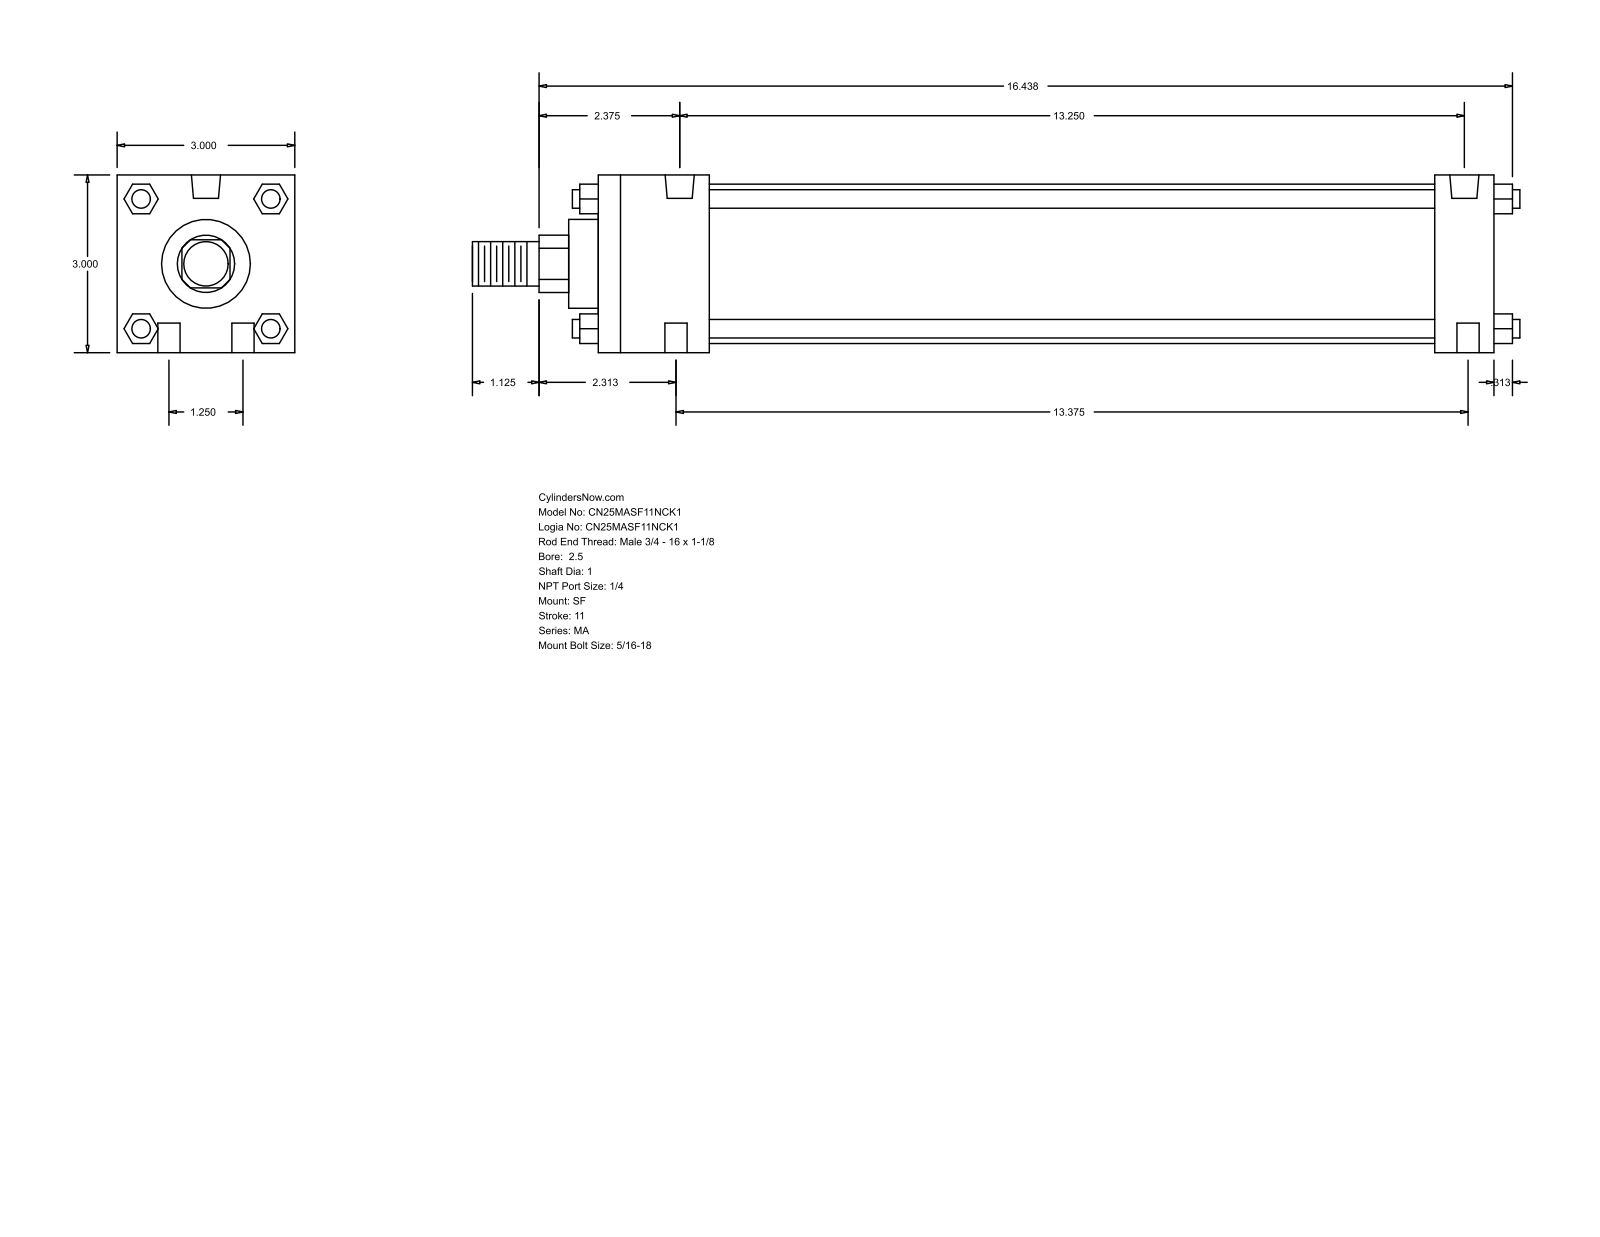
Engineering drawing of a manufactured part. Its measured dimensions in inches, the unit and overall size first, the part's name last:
Units: inches
Overall size (bounding box): 17.687 × 3 × 3
Round holes (diameter × count): ⌀0.375 ×4, ⌀0.313 ×2, ⌀0.492 ×2
Round bosses / shafts (diameter × count): ⌀0.313 ×4, ⌀2.69 ×1, ⌀1.5 ×1, ⌀1 ×1, ⌀0.75 ×1
Partial cylindrical surfaces — rounded edges, fillets, slot ends (radius × count): R0.484 ×1
Main face-to-face distances: 3, 15.125, 0.5, 14.125, 1, 1.875, 12.25, 13.25, 1.095, 1.896
Hole centre spacings: 0.628, 1.25, 13.25, 13.327, 13.327, 13.375, 13.433
Bodies: 0 solids, 124 faces (94 planar, 30 cylindrical, 0 other)
Part name (STEP PRODUCT): MA_SF__0250_1
STEP written by: GSSL Pune (CONFIG_CONTROL_DESIGN)
